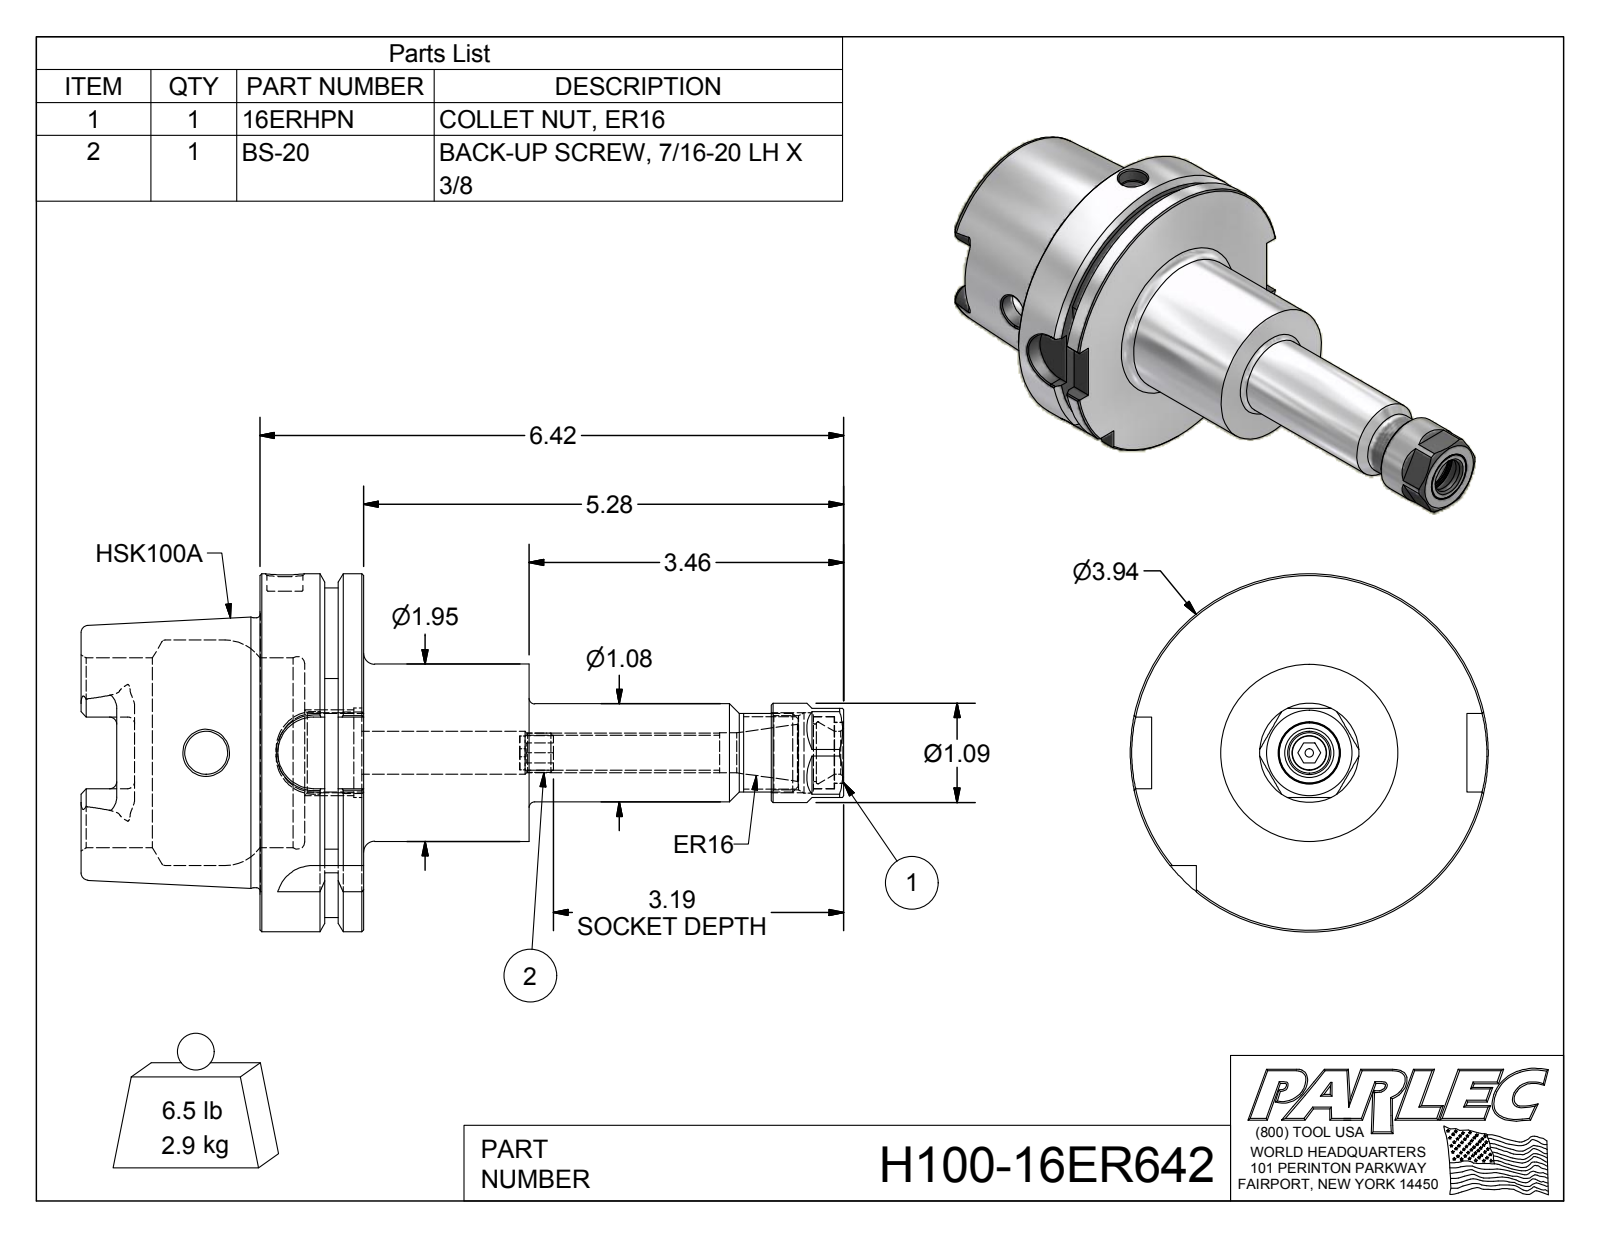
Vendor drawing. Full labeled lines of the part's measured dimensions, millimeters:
Part name (STEP PRODUCT): H100-16ER642; H100-16ER6-1; BS-20; 16ERHPN
STEP written by: Autodesk Inventor 2012 (AUTOMOTIVE_DESIGN)
Units: millimetres
Bodies: 4 solids, 191 faces (74 planar, 50 cylindrical, 67 other)
Overall size (bounding box): 213.1 × 100 × 100
Volume: 378 200 mm³ · Surface area: 72 580 mm²
Round holes (diameter × count): ⌀12 ×2, ⌀2.3 ×1, ⌀9.7 ×1, ⌀10 ×1, ⌀11.2 ×1, ⌀12 ×1, ⌀12 ×1, ⌀16 ×1, ⌀17.1 ×1, ⌀17.3 ×1, ⌀20.2 ×1, ⌀20.7 ×1
Round bosses / shafts (diameter × count): ⌀100 ×1, ⌀75.4 ×1, ⌀49.5 ×1, ⌀27.7 ×1, ⌀27.4 ×1, ⌀22 ×1, ⌀20.1 ×1, ⌀17 ×1
Partial cylindrical surfaces — rounded edges, fillets, slot ends (radius × count): R2 ×6, R4.9 ×4, R10 ×4, R46 ×1
Main face-to-face distances: 29, 12.5, 16.5, 75.2, 62.7, 46.2, 50, 62.5, 79, 125.2
